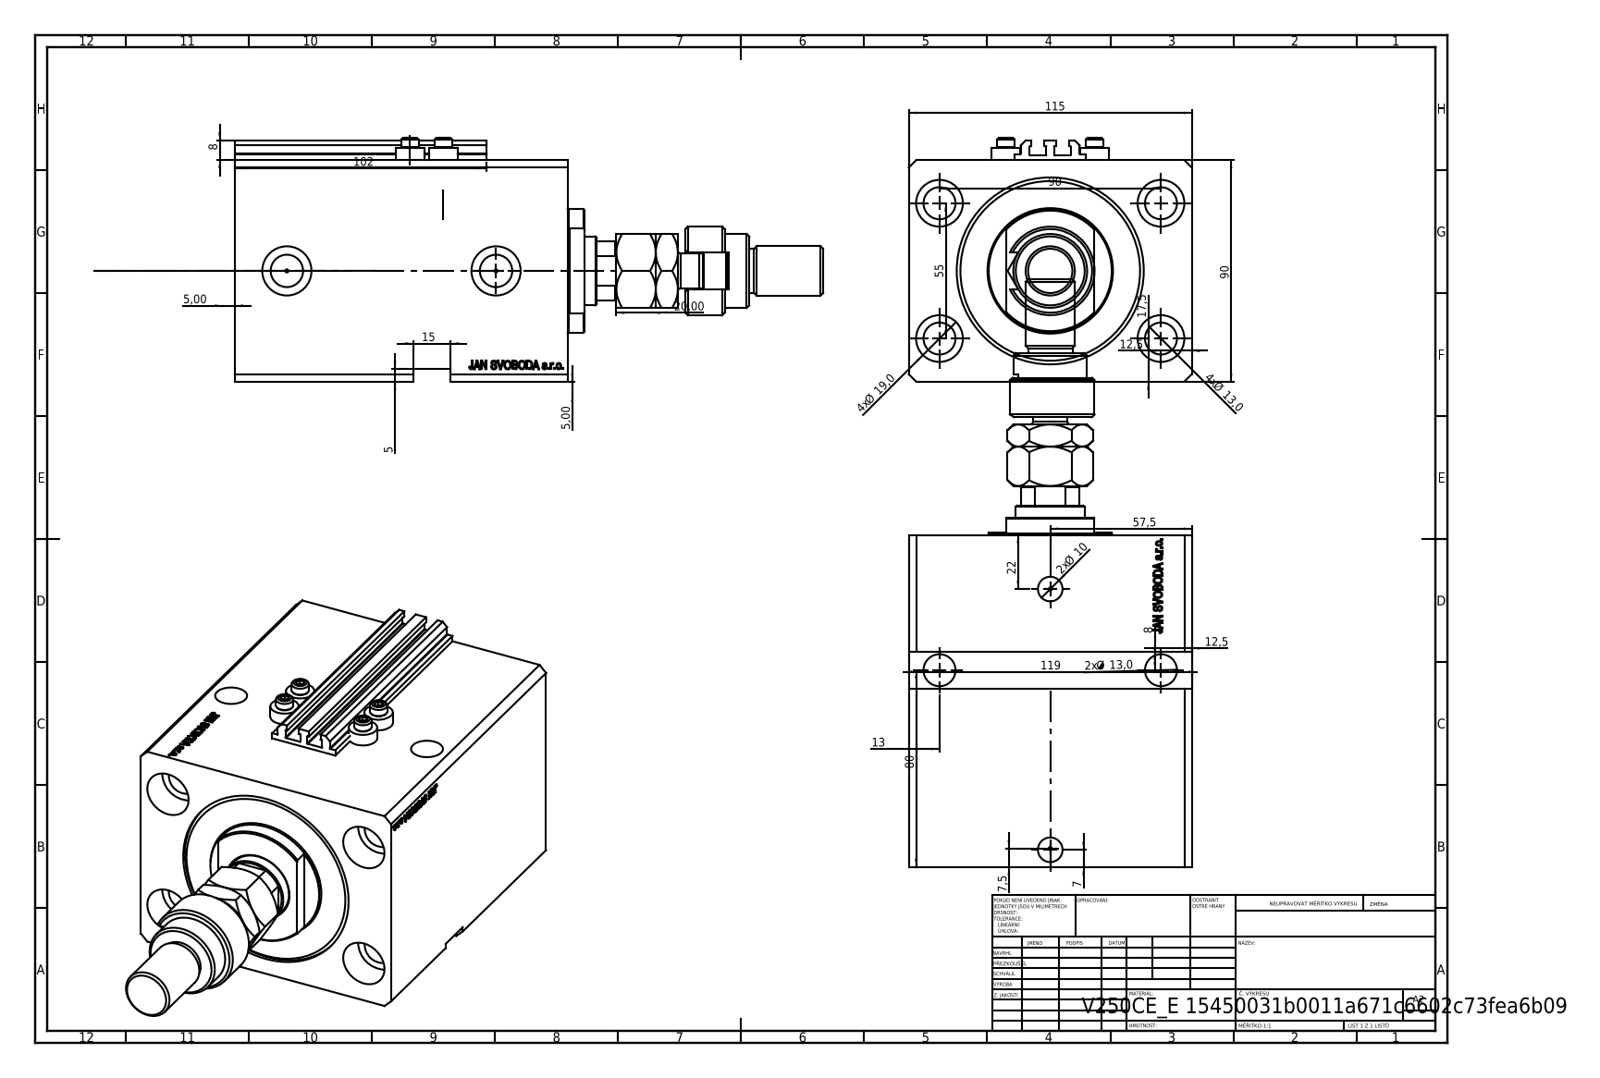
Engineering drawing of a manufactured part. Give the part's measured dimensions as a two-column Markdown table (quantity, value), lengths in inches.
| quantity | value |
| --- | --- |
| part name | MFA; V250CE_E_Body; V250CE_VC_E; V250CE_C_VCP (+2 more) |
| STEP written by | SolidWorks 2019 (CONFIG_CONTROL_DESIGN) |
| units | inches |
| bodies | 10 solids, 1192 faces (571 planar, 139 cylindrical, 482 other) |
| overall size | 9.406 × 4.528 × 3.898 |
| volume | 74.82 in³ |
| surface area | 307.4 in² |
| round holes (diameter × count) | 0.512 × 6, 0.049 × 4, 0.157 × 4, 0.748 × 4, 0.394 × 2, 0.518 × 2, 0.787 × 2, 0.728 × 1, 1.102 × 1, 2.48 × 1, 2.992 × 1 |
| round bosses / shafts (diameter × count) | 0.457 × 4, 0.276 × 4, 1.969 × 1, 1.417 × 1, 1.181 × 1, 0.866 × 1, 0.787 × 1, 0.709 × 1 |
| partial cylindrical surfaces (radius × count) | 0.008 × 10, 0.295 × 1, 0.472 × 1, 0.531 × 1 |
| main face-to-face distances | 3.543, 4.528, 5.315, 3.425, 0.705, 4.61, 4.13, 1.185, 1.969, 2.161 |
| hole center spacings | 2.076, 3.543, 0.535, 1.078, 1.12, 1.324, 1.417, 1.515 |
